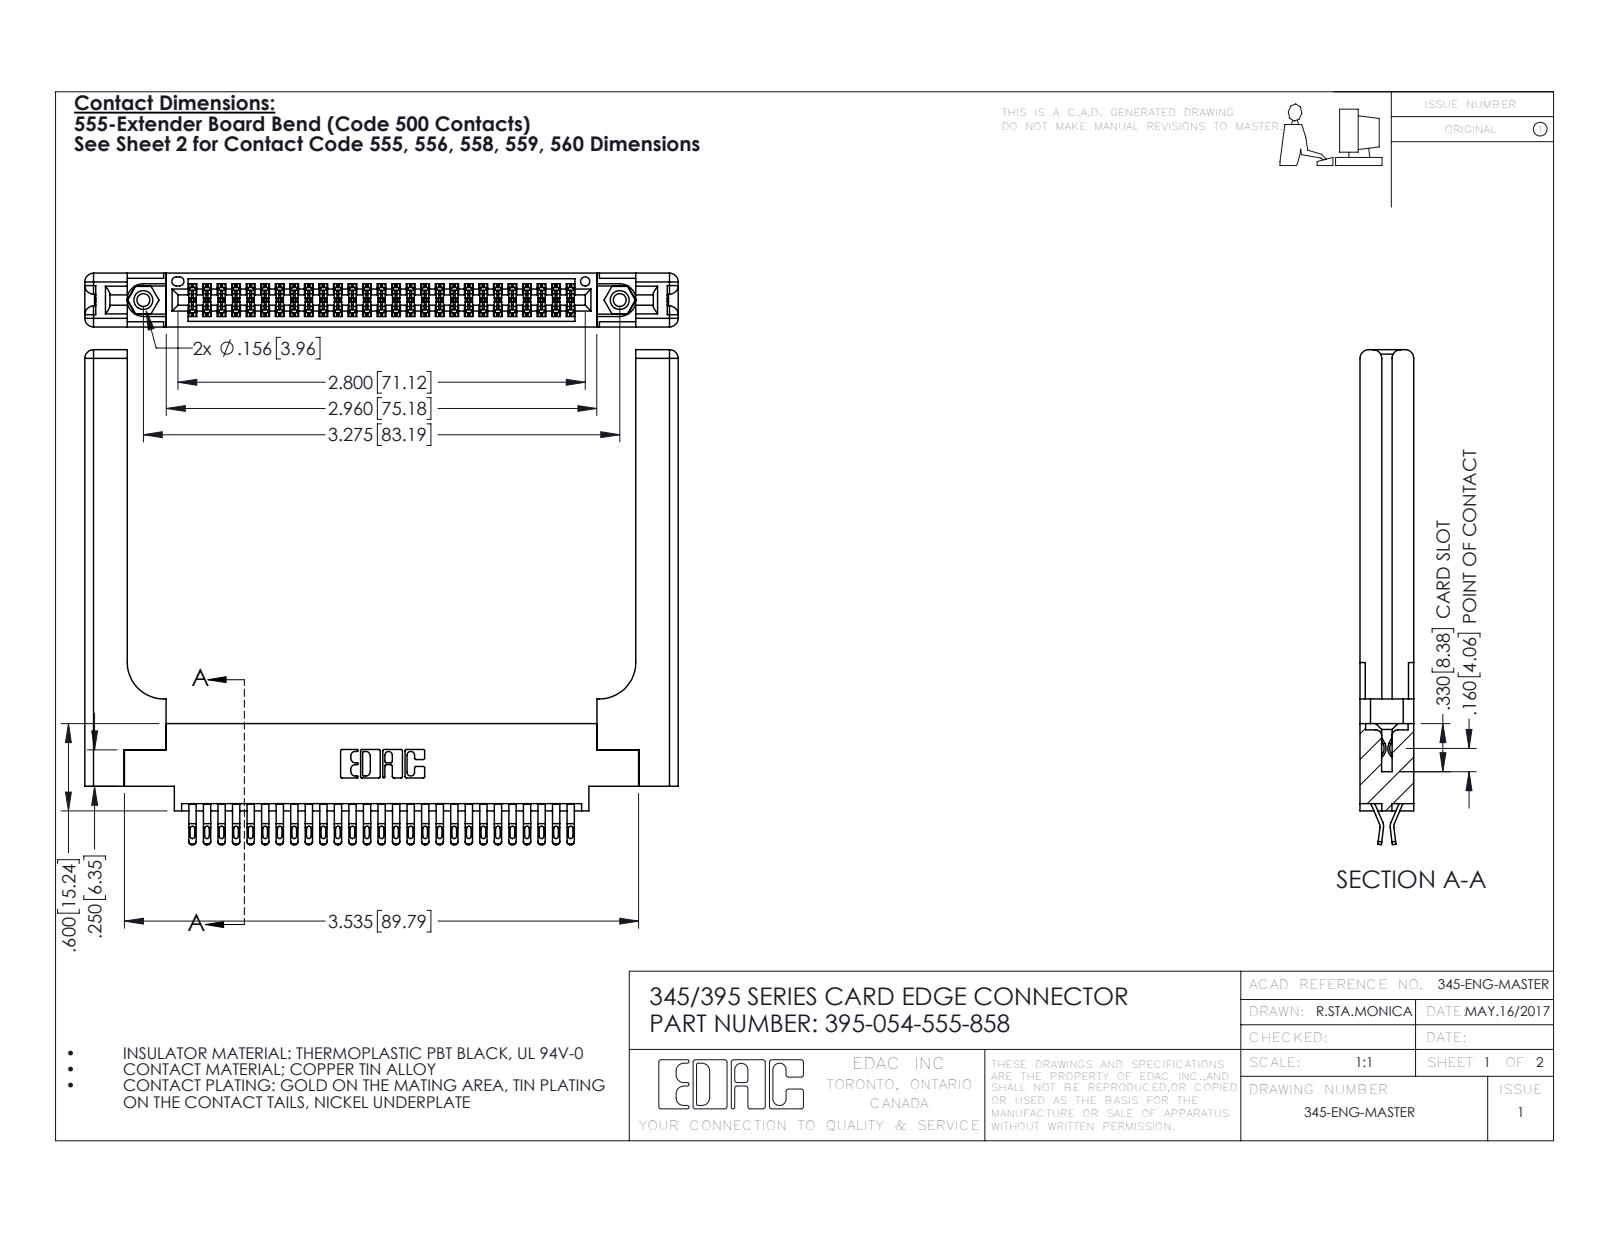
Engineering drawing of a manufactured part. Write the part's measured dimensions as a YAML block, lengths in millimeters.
part_name: "345 Part_0.170 Offset - 0.156 Dia-TH; 395-054-555-858; 345-292-001_555 Tail; 345-220-058_345-220-058 (+1 more)"
step_written_by: "SolidWorks 2016 (CONFIG_CONTROL_DESIGN)"
units: millimeters
bodies: {solids: 59, faces: 3410, planar: 1906, cylindrical: 1444, other: 60}
overall_size: [103.6, 86.4, 9.4]
volume: 18440
surface_area: 20190
round_holes:
  - {diameter: 2.3, count: 2}
  - {diameter: 3.2, count: 2}
  - {diameter: 4, count: 2}
  - {diameter: 1.6, count: 1}
round_bosses_or_shafts:
  - {diameter: 3.9, count: 2}
partial_cylinders:
  - {radius: 0.4, count: 135}
  - {radius: 0.5, count: 108}
  - {radius: 0.2, count: 81}
  - {radius: 0.3, count: 22}
  - {radius: 1.5, count: 16}
  - {radius: 0.2, count: 6}
  - {radius: 0.8, count: 6}
  - {radius: 0.7, count: 3}
face_to_face_distances: [9.4, 1.8, 7.6, 0.6, 5.7, 3.8, 3.8, 2.5, 6.9, 5.1]
hole_center_spacings: [6.9, 77.2, 83.2]
